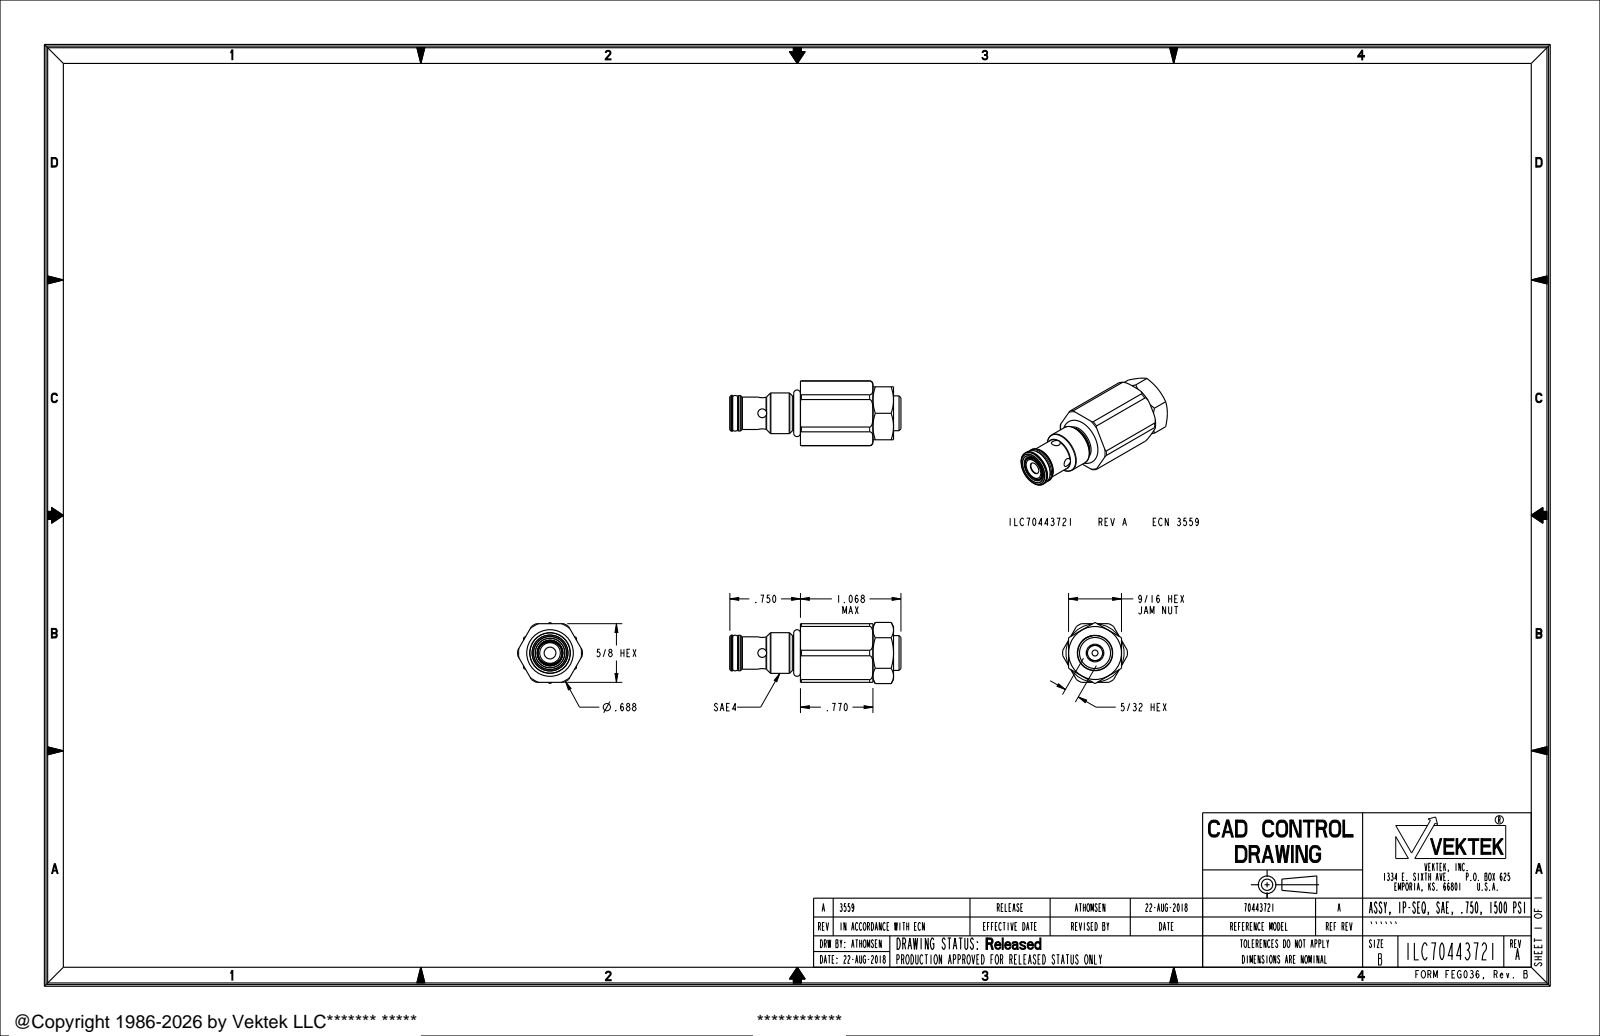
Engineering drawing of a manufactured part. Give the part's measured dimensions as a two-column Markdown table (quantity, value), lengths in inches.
| quantity | value |
| --- | --- |
| part name | ILC70443721 |
| STEP written by | PRO/ENGINEER BY PARAMETRIC TECHNOLOGY CORPORATION, 2013320 (AUTOMOTIVE_DESIGN) |
| units | inches |
| bodies | 1 solid, 214 faces (45 planar, 69 cylindrical, 100 other) |
| overall size | 1.818 × 0.688 × 0.65 |
| volume | 0.402 in³ |
| surface area | 4.717 in² |
| round holes (diameter × count) | 0.093 × 2, 0.125 × 1, 0.161 × 1, 0.247 × 1, 0.27 × 1, 0.375 × 1, 0.5 × 1, 0.528 × 1 |
| round bosses / shafts (diameter × count) | 0.432 × 1, 0.382 × 1, 0.377 × 1, 0.37 × 1, 0.364 × 1, 0.344 × 1, 0.236 × 1 |
| partial cylindrical surfaces (radius × count) | 0.115 × 2, 0.094 × 1, 0.344 × 1 |
| main face-to-face distances | 0.623, 0.562, 0.77, 0.219, 0.989, 0.052, 0.27, 0.718, 0.079, 0.298 |
